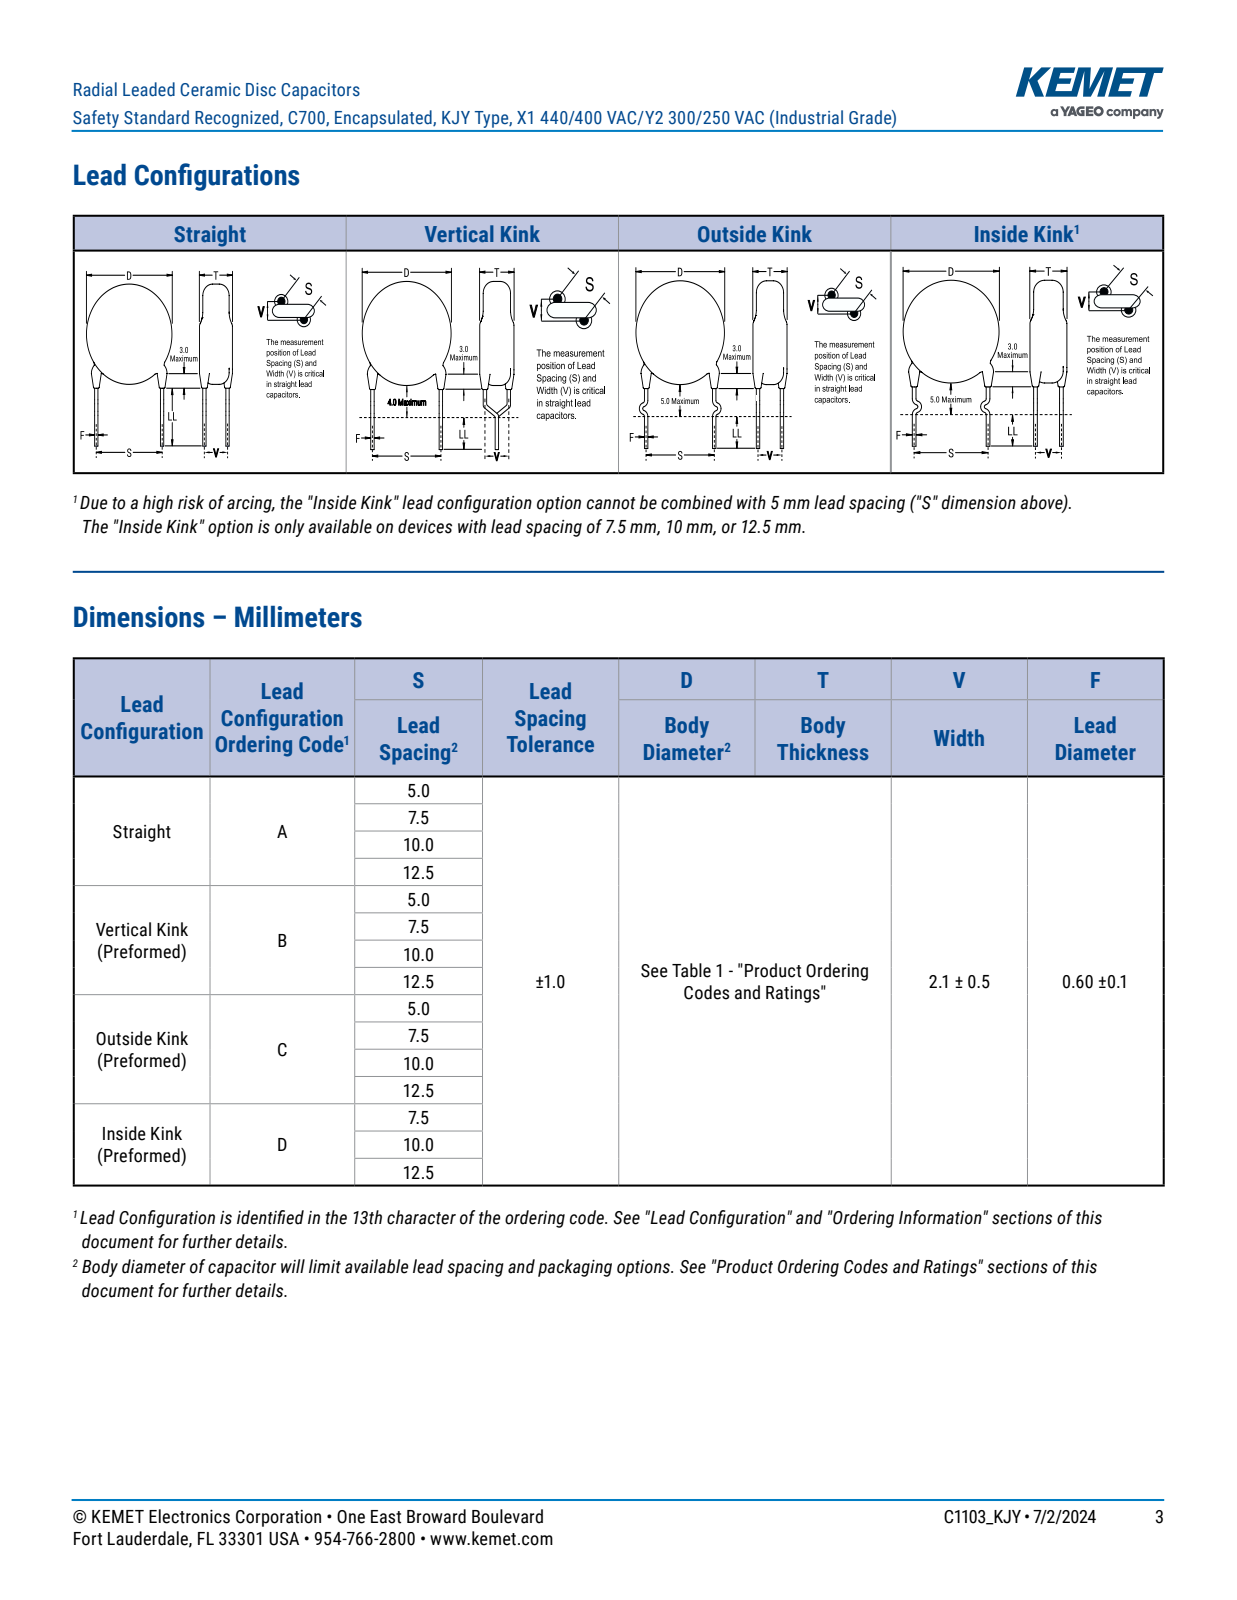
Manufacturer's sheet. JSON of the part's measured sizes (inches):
{"part_name": "CCD_KST_10X5_D10T5S7.5LL25F0.7V2.1", "step_written_by": "SolidWorks 2021 (AUTOMOTIVE_DESIGN)", "units": "inches", "bodies": {"solids": 4, "faces": 80, "planar": 63, "cylindrical": 13, "other": 4}, "overall_size": [1.422, 0.394, 0.197], "volume_in3": 0.025, "surface_area_in2": 0.659, "round_bosses_or_shafts": [[0.047, 2], [0.028, 2], [0.394, 1]], "partial_cylinders_radius": [[0.024, 2]], "face_to_face_distances": [0.197, 0.984, 1.253, 0.269, 1.207, 0.223, 0.046, 0.013, 0.037, 0.02]}
